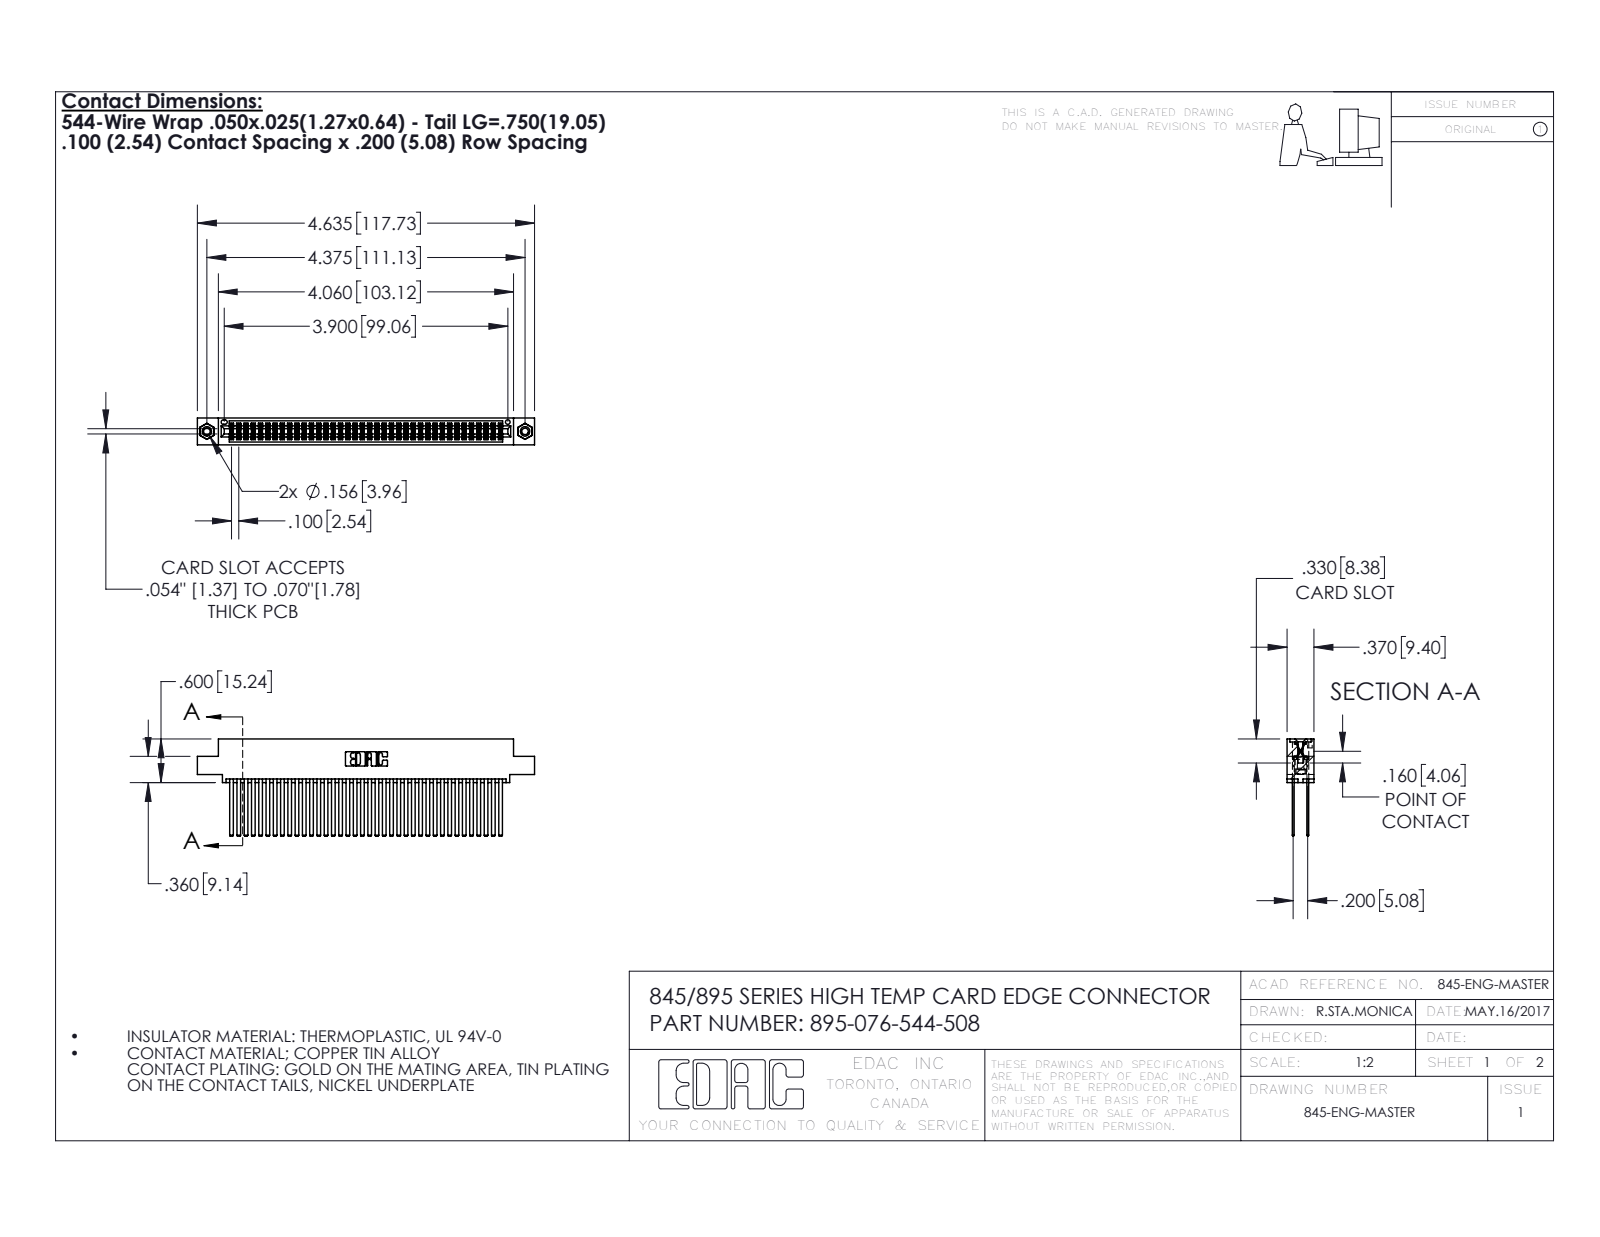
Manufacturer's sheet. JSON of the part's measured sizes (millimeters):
{"part_name": "345 Part_0.110 Offset - 0.156 Dia-TI; 395-076-544-508; 345-292-001_345-293-144; 345-250-001_345-250-003-102", "step_written_by": "SolidWorks 2016 (CONFIG_CONTROL_DESIGN)", "units": "millimeters", "bodies": {"solids": 79, "faces": 3534, "planar": 2320, "cylindrical": 1198, "other": 16}, "overall_size": [117.7, 34, 9.4], "volume_mm3": 12400, "surface_area_mm2": 21460, "round_holes": [[2.3, 2], [3.2, 2], [4, 2], [1.6, 1]], "round_bosses_or_shafts": [[3.9, 2]], "partial_cylinders_radius": [[0.2, 114], [0.3, 22], [0.2, 6], [0.8, 6], [0.7, 3], [0.4, 2], [0.5, 2], [0.6, 2]], "face_to_face_distances": [5.1, 0.6, 1.8, 2.5, 6.9, 7.6, 5.7, 4.4, 9.4, 1.3], "hole_center_spacings": [6.9, 105.1, 111.1]}
